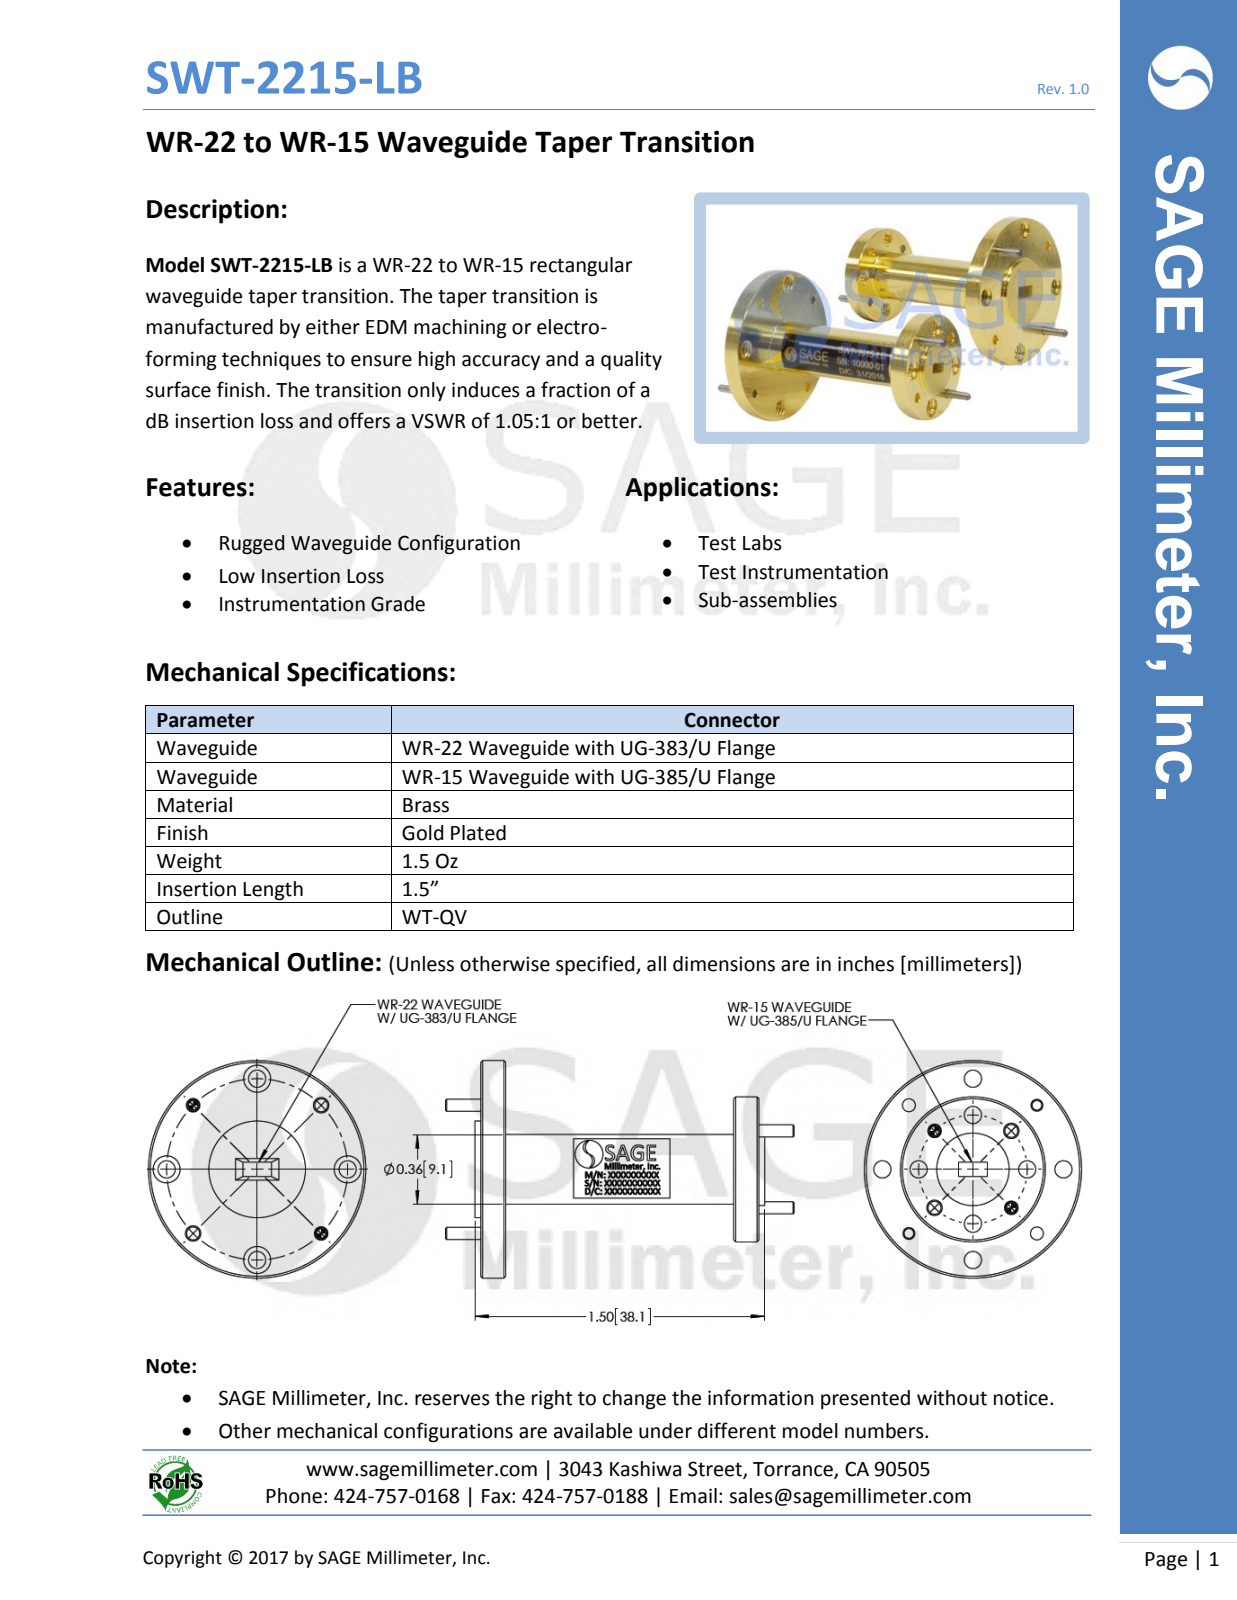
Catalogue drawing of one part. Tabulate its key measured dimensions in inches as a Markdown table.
| quantity | value |
| --- | --- |
| part name | SWT-2215-LB |
| STEP written by | SolidWorks 2016 (CONFIG_CONTROL_DESIGN) |
| units | inches |
| bodies | 5 solids, 138 faces (32 planar, 66 cylindrical, 40 other) |
| overall size | 1.82 × 1.125 × 1.125 |
| volume | 0.318 in³ |
| surface area | 5.456 in² |
| round holes (diameter × count) | 0.089 × 8, 0.14 × 8, 0.061 × 4, 0.067 × 4 |
| round bosses / shafts (diameter × count) | 0.063 × 4, 1.125 × 1, 0.75 × 1, 0.5 × 1, 0.375 × 1 |
| main face-to-face distances | 0.13, 1.31, 0.16, 0.03, 1.34, 1.47, 1.18, 1.44, 1.5, 0.05 |
| hole center spacings | 0.335, 0.547, 0.188, 0.215, 0.359, 0.398, 0.519, 0.663 |
